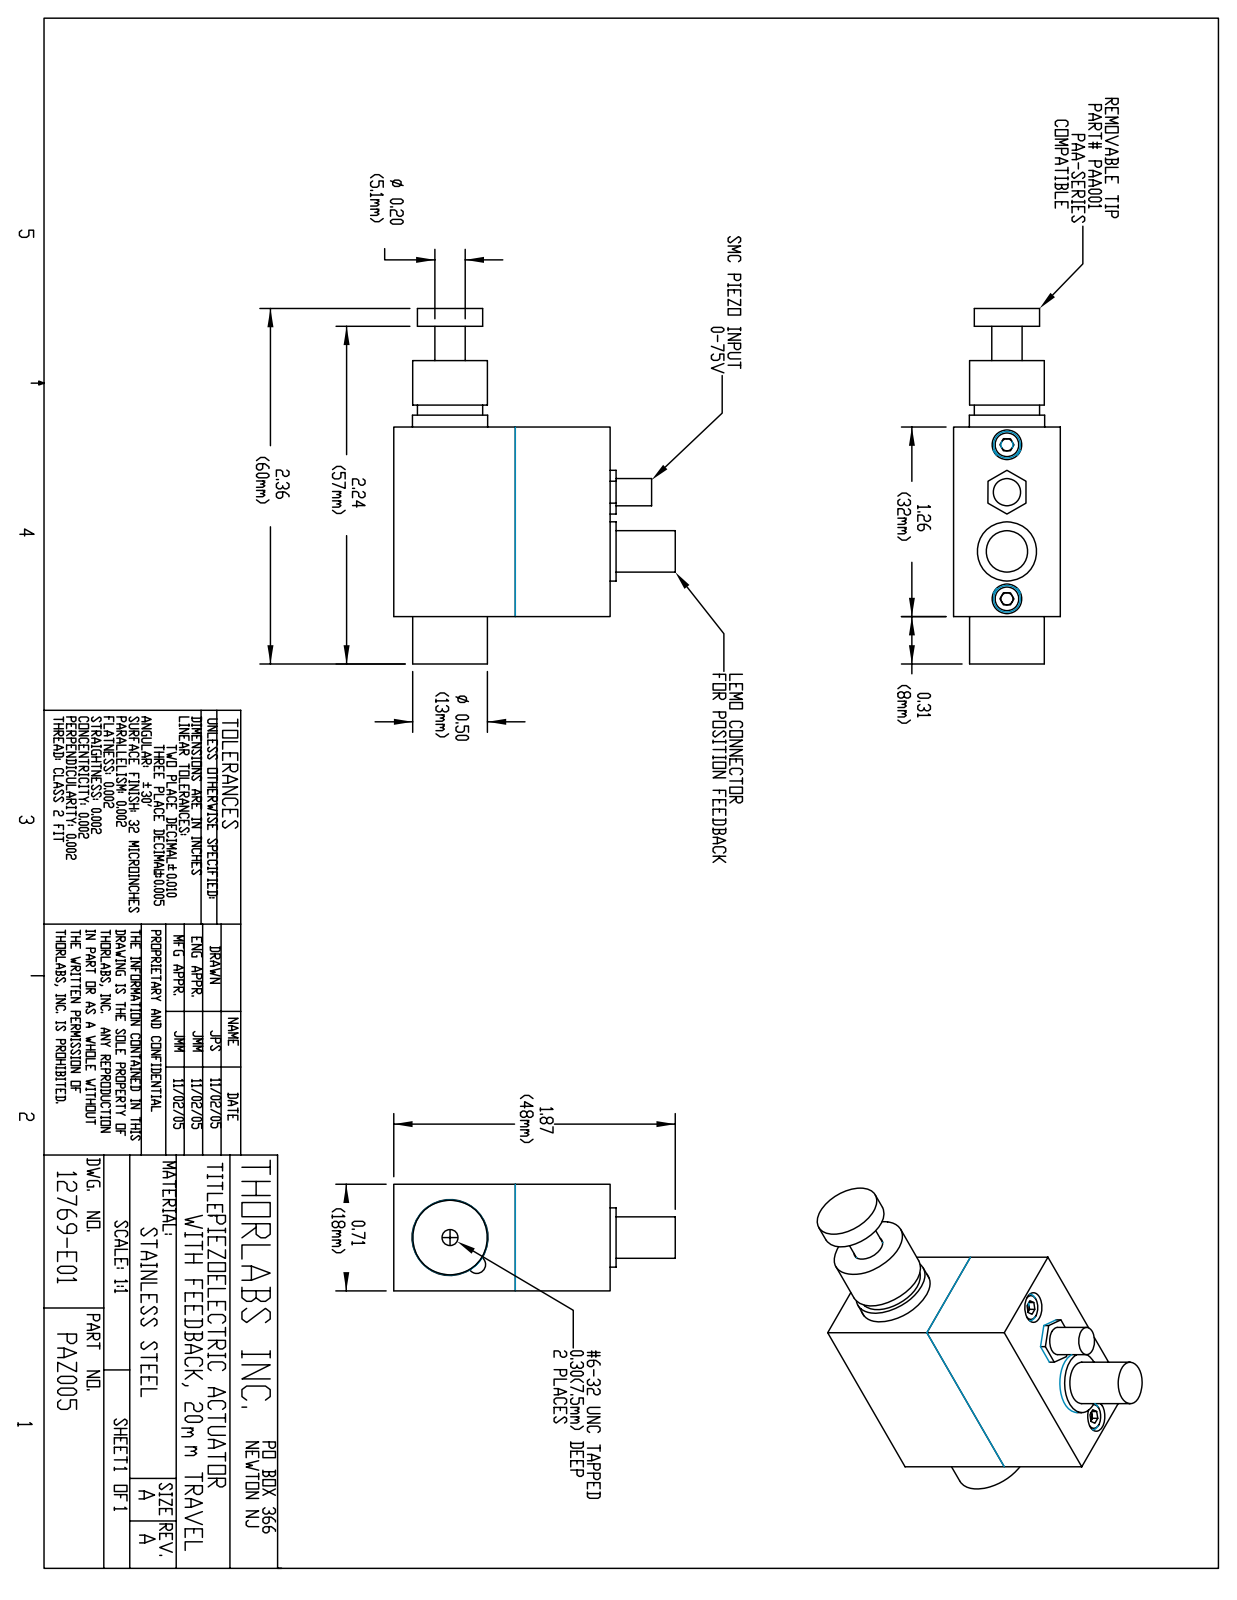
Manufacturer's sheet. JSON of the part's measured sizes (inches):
{"part_name": "12769-E0W", "step_written_by": "SolidWorks 2007 (AUTOMOTIVE_DESIGN)", "units": "inches", "bodies": {"solids": 0, "faces": 109, "planar": 63, "cylindrical": 36, "other": 10}, "overall_size": [2.362, 1.87, 0.709], "round_holes": [[0.098, 2], [0.197, 2], [0.107, 1], [0.209, 1], [0.504, 1]], "round_bosses_or_shafts": [[0.5, 1], [0.496, 1], [0.433, 1], [0.394, 1], [0.276, 1], [0.201, 1], [0.181, 1]], "partial_cylinders_radius": [[0.059, 1]], "face_to_face_distances": [0.709, 1.26, 1.437, 0.807, 0.63, 0.669, 1.575, 0.315, 0.441, 1.701], "hole_center_spacings": [1.024]}
